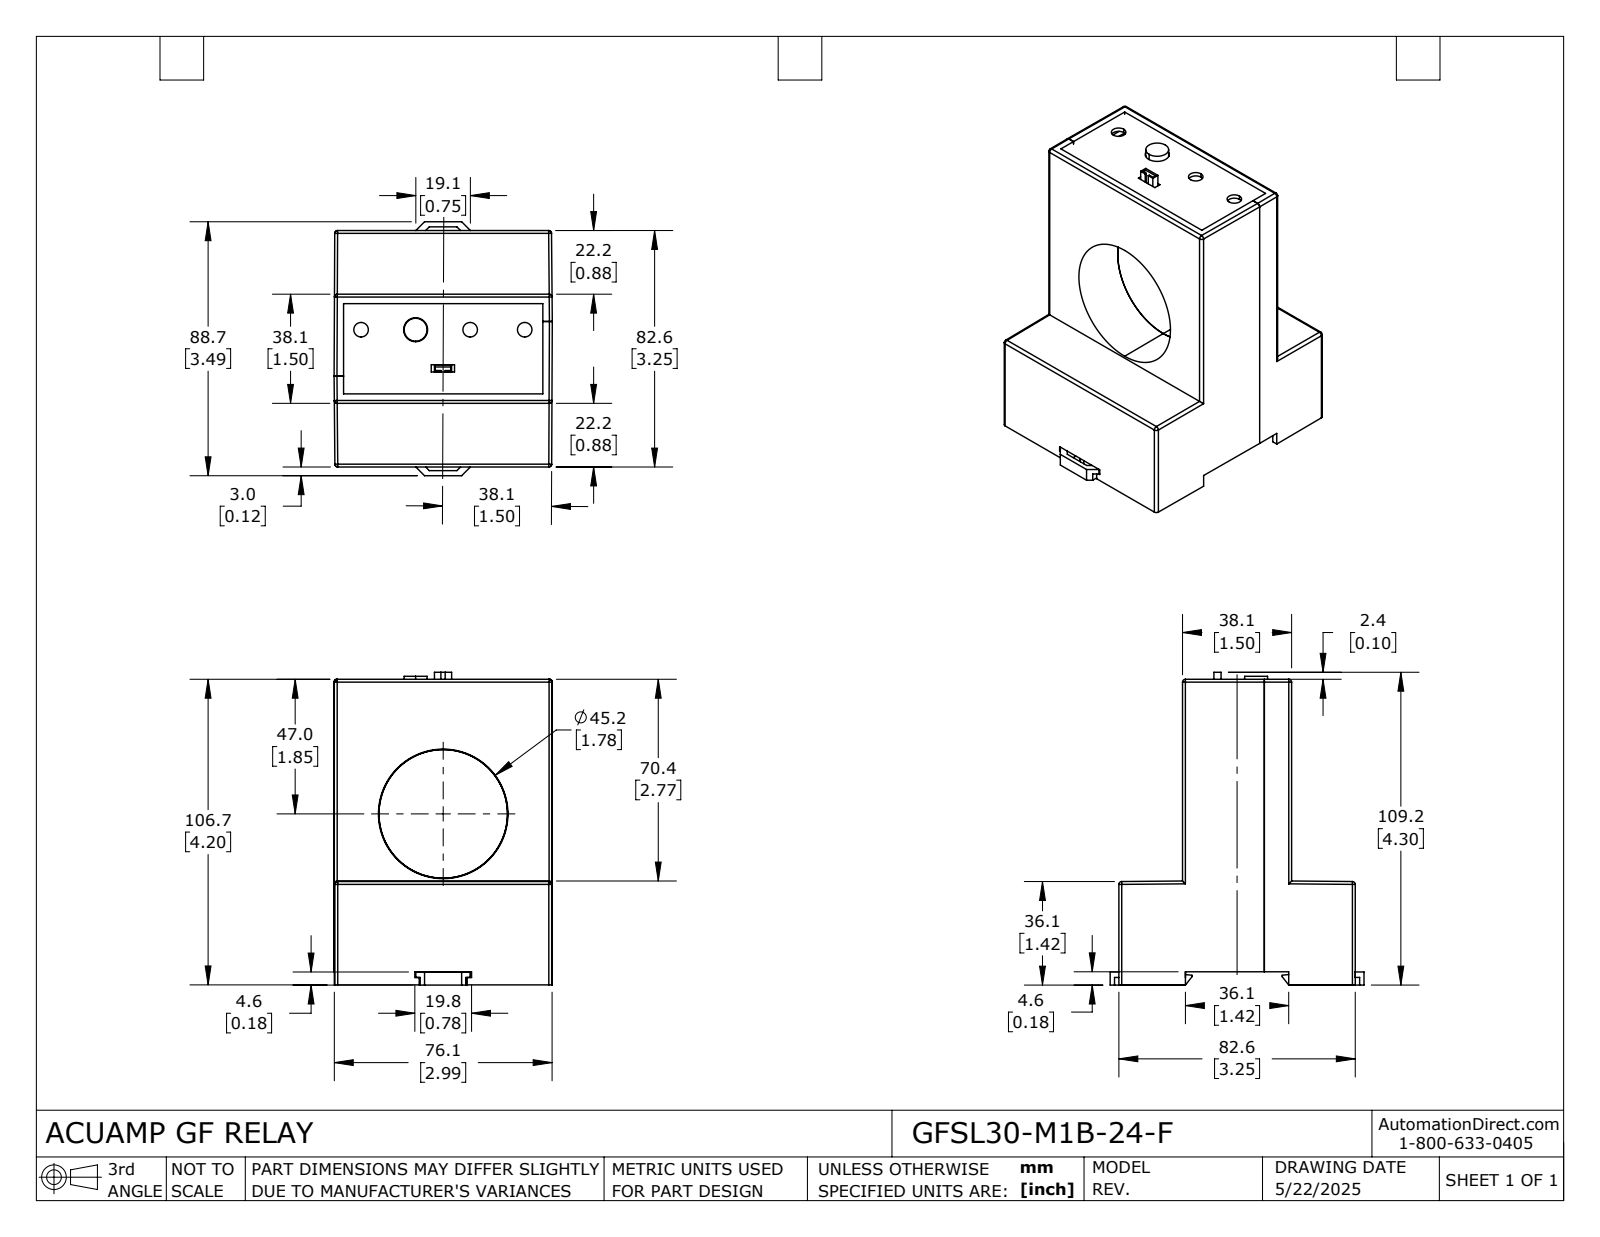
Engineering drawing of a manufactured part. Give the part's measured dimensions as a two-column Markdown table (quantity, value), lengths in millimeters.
| quantity | value |
| --- | --- |
| part name | GFSL30-M1B-24-F |
| STEP written by | SolidWorks 2024 (AUTOMOTIVE_DESIGN) |
| units | millimeters |
| bodies | 8 solids, 1046 faces (890 planar, 120 cylindrical, 36 other) |
| overall size | 109.2 × 88.6 × 76.2 |
| volume | 90 690 mm³ |
| surface area | 99 290 mm² |
| round holes (diameter × count) | 5.1 × 7, 8.4 × 4, 3 × 2 |
| round bosses / shafts (diameter × count) | 2.5 × 2, 8 × 1 |
| partial cylindrical surfaces (radius × count) | 0.5 × 23, 1 × 20, 0.2 × 4, 0.3 × 4, 2.6 × 4, 4.6 × 4 |
| main face-to-face distances | 2, 22.2, 58.3, 36.1, 74.1, 2, 76.1, 38.1, 20.2, 56.3 |
| hole center spacings | 19.1, 23.3, 38.1, 13.5, 40.4, 57.2, 58.7, 25.2 |
